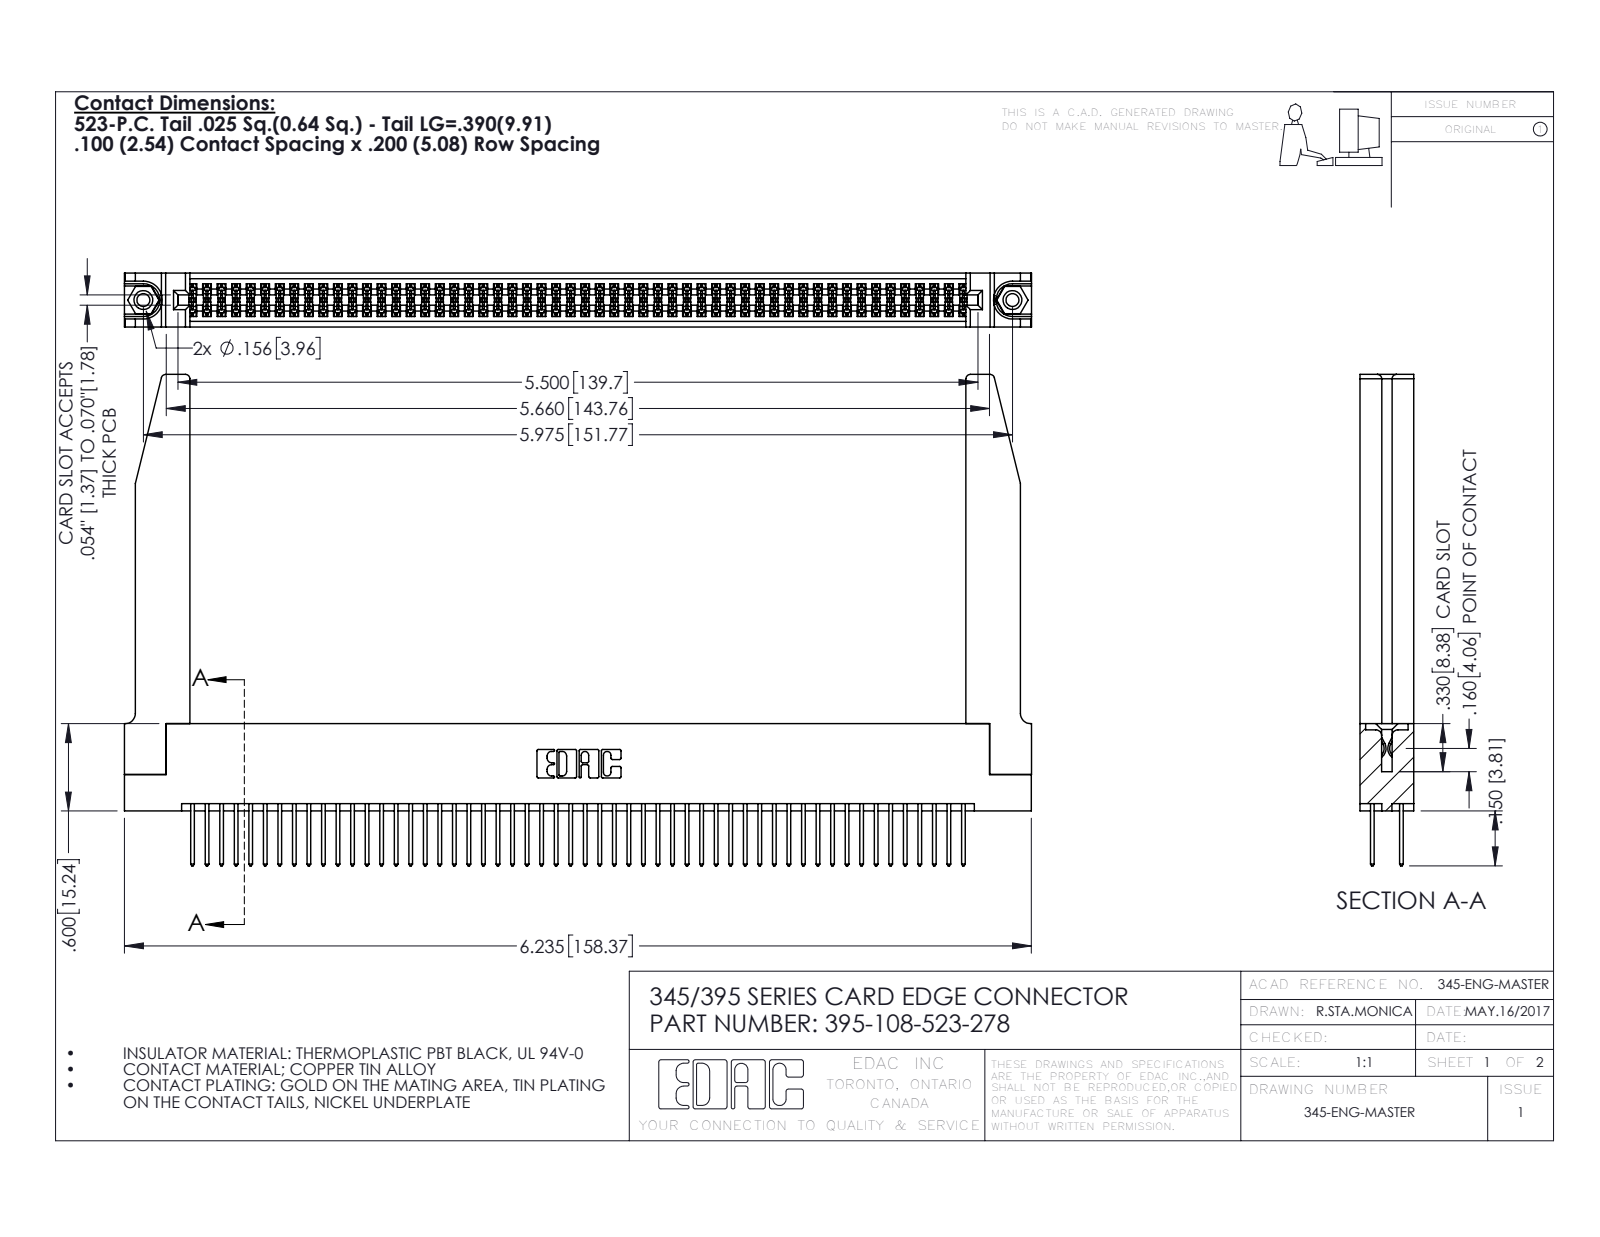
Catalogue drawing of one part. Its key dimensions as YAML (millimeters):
part_name: "345-250-001_345-250-001-102; 345-292-001_345-293-123; 395-108-523-278; 345-220-078_345-220-078 (+1 more)"
step_written_by: "SolidWorks 2016 (CONFIG_CONTROL_DESIGN)"
units: millimeters
bodies: {solids: 113, faces: 5760, planar: 3786, cylindrical: 1922, other: 52}
overall_size: [158.4, 85.8, 9.4]
volume: 23480
surface_area: 31300
round_holes:
  - {diameter: 2.3, count: 2}
  - {diameter: 3.2, count: 2}
  - {diameter: 4, count: 2}
  - {diameter: 1.6, count: 1}
round_bosses_or_shafts:
  - {diameter: 3.9, count: 2}
partial_cylinders:
  - {radius: 0.2, count: 162}
  - {radius: 0.3, count: 108}
  - {radius: 0.3, count: 22}
  - {radius: 0.8, count: 8}
  - {radius: 0.2, count: 6}
  - {radius: 0.8, count: 6}
  - {radius: 0.7, count: 3}
  - {radius: 0.4, count: 2}
face_to_face_distances: [1.8, 7.6, 9.4, 5.1, 2.5, 6.9, 0.6, 5.7, 4.4, 3.8]
hole_center_spacings: [6.9, 145.8, 151.8]
